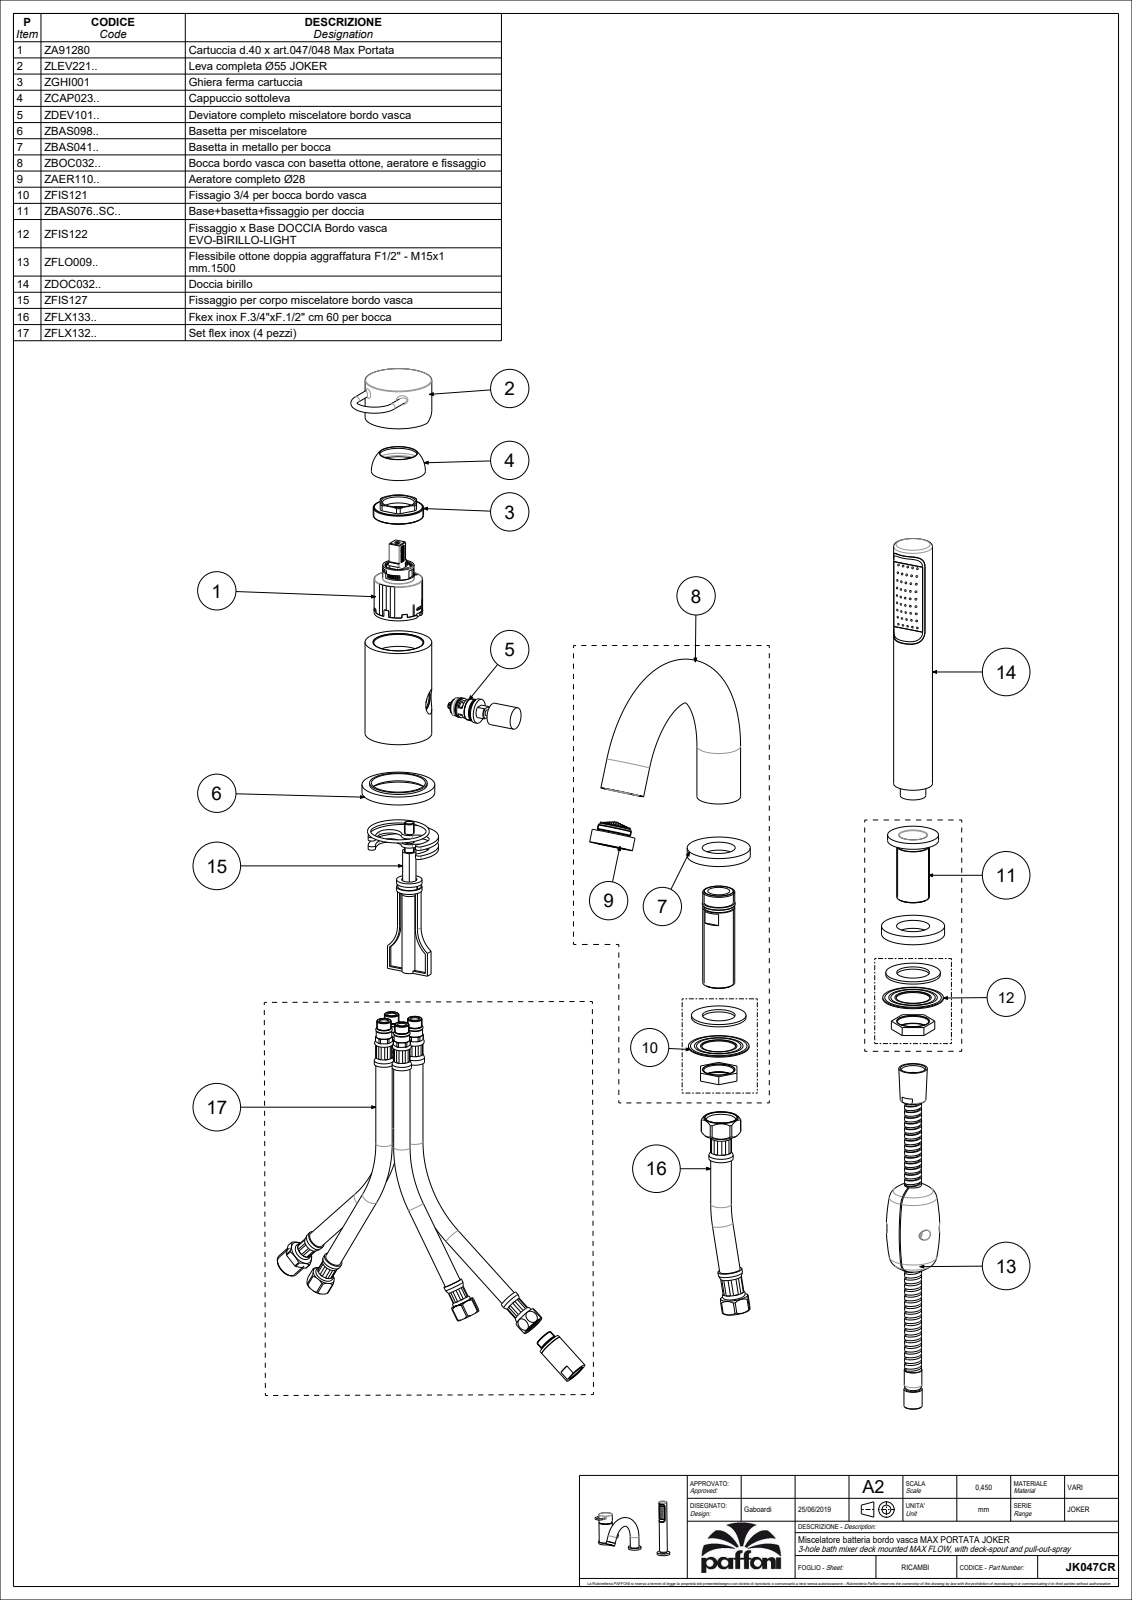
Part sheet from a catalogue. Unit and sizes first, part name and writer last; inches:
Units: inches
Overall size (bounding box): 14.016 × 8.74 × 8.261
Round holes (diameter × count): ⌀0.02 ×61, ⌀0.059 ×45, ⌀0.315 ×5, ⌀0.433 ×4, ⌀0.512 ×4, ⌀0.13 ×2, ⌀0.197 ×2, ⌀0.276 ×2, ⌀0.295 ×2, ⌀0.386 ×2, ⌀1.071 ×2, ⌀1.299 ×2
Round bosses / shafts (diameter × count): ⌀0.197 ×4, ⌀2.165 ×2, ⌀2.047 ×2, ⌀1.74 ×2, ⌀1.417 ×2, ⌀1.335 ×2, ⌀0.504 ×2, ⌀0.413 ×2
Partial cylindrical surfaces — rounded edges, fillets, slot ends (radius × count): R0.01 ×39, R0.02 ×21, R0.006 ×12, R0.008 ×12, R0.059 ×11, R0.043 ×10, R0.079 ×8, R0.118 ×8
Main face-to-face distances: 0.276, 0.079, 0.394, 0.059, 0.197, 4.697, 4.421, 0.472, 0.354, 0.118
Hole centre spacings: 0.311, 0.542, 0.788, 0.256, 0.15, 0.226, 0.512, 1.039
Volume: 21.18 in³ · Surface area: 326.4 in²
Bodies: 6 solids, 2520 faces (1395 planar, 732 cylindrical, 393 other)
Part name (STEP PRODUCT): JK047CR
STEP written by: CREO PARAMETRIC BY PTC INC, 2020044 (CONFIG_CONTROL_DESIGN)
